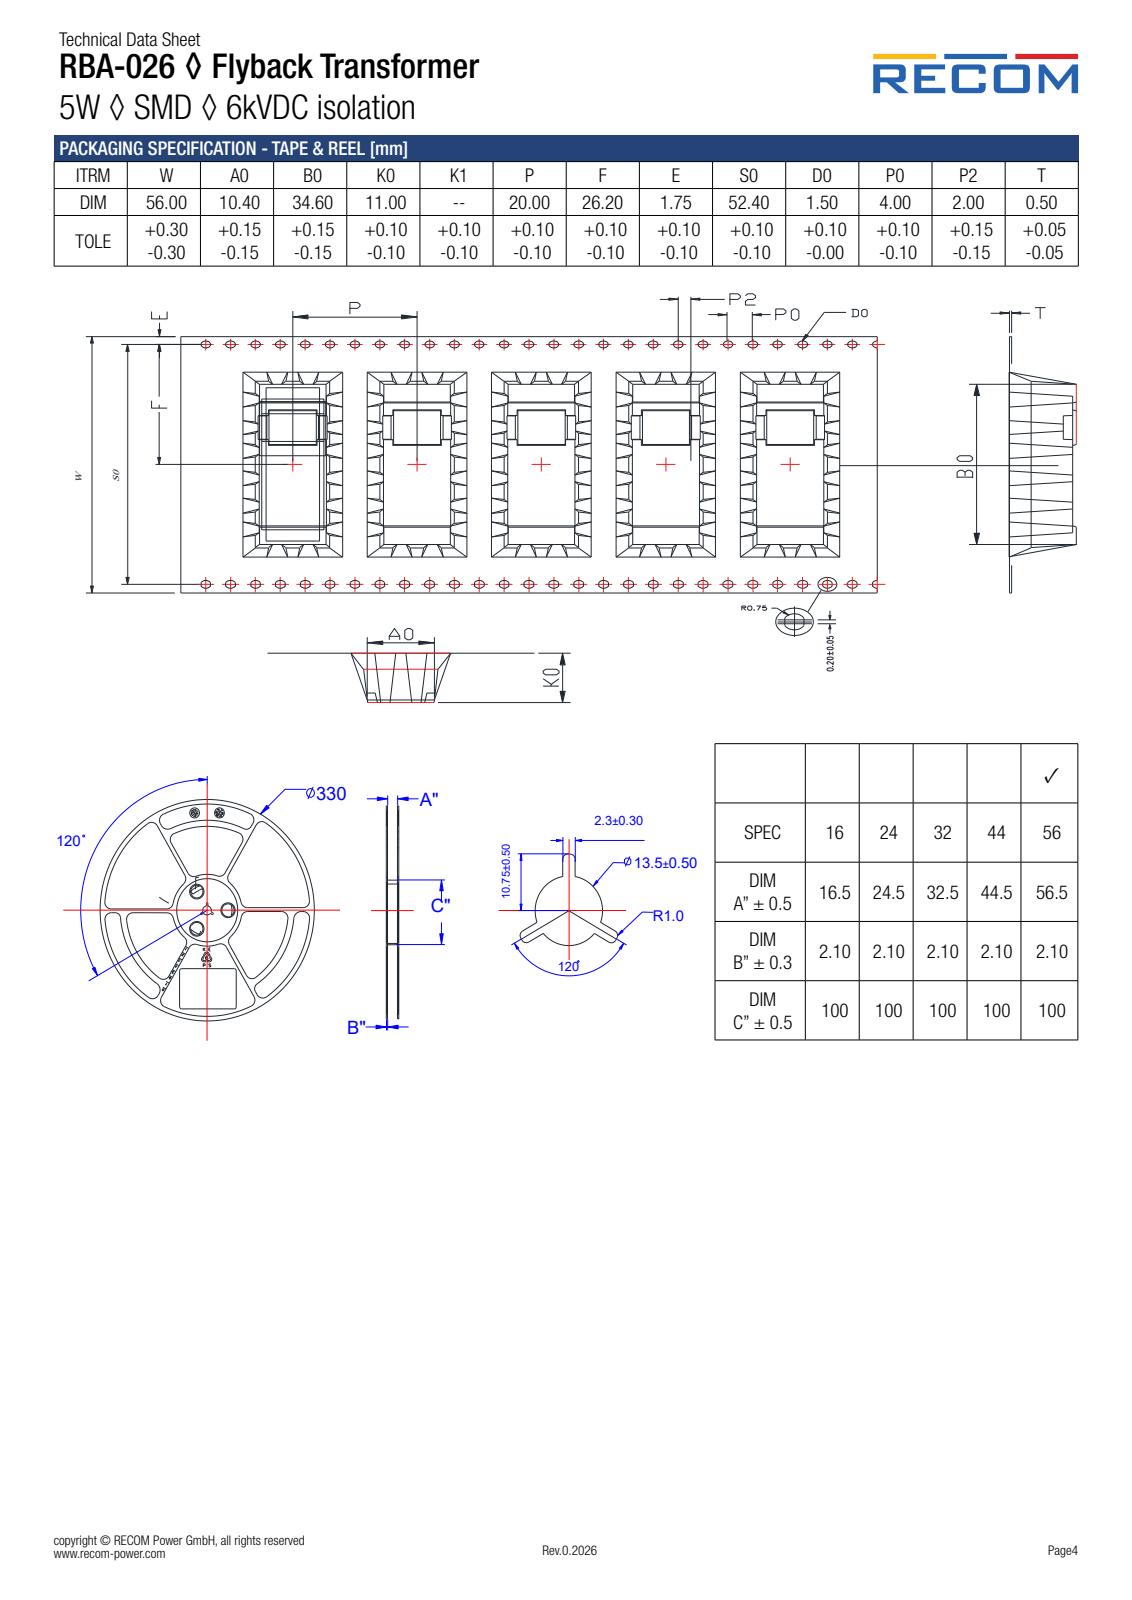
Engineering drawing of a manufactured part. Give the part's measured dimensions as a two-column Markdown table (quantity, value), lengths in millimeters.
| quantity | value |
| --- | --- |
| part name | RBA-026-CORE_默认; RBA-026-PIN_默认; RBA-026-Bobbin_默认; RBA-026 |
| STEP written by | SolidWorks 2024 (AUTOMOTIVE_DESIGN) |
| units | millimeters |
| bodies | 11 solids, 168 faces (124 planar, 44 cylindrical, 0 other) |
| overall size | 34.5 × 11 × 11 |
| volume | 1 522 mm³ |
| surface area | 1 853 mm² |
| partial cylindrical surfaces (radius × count) | 0.5 × 8, 0.2 × 4, 0.3 × 4, 0.4 × 2 |
| main face-to-face distances | 2.4, 1.07, 9.92, 1, 11, 9.99, 8.92, 0.65, 10.35, 1.7 |
